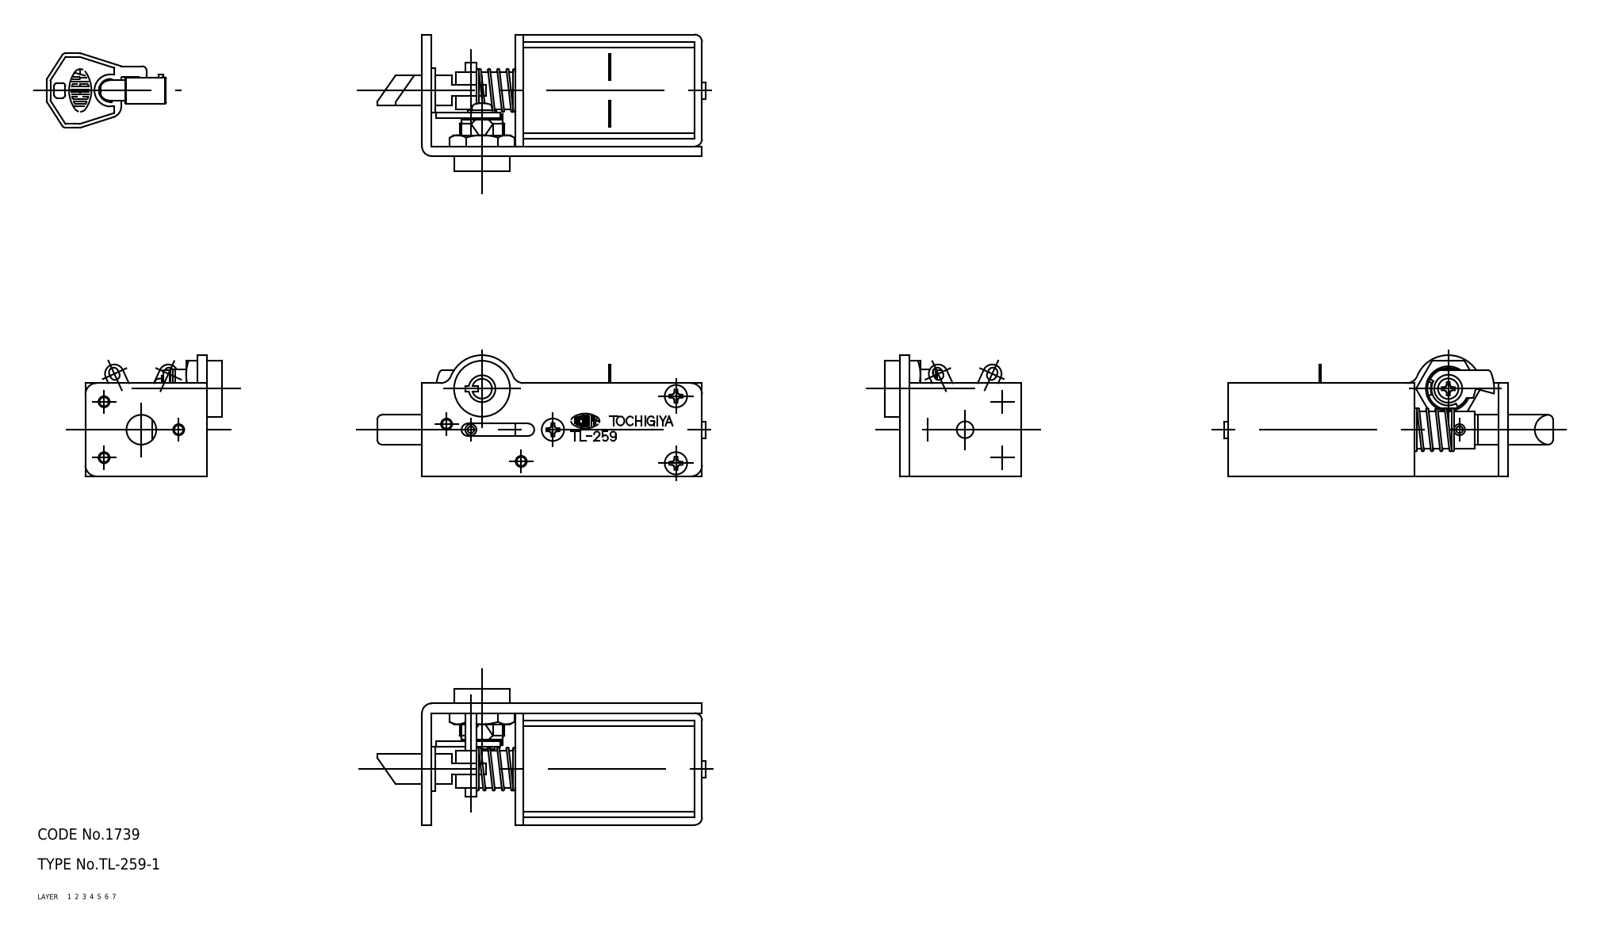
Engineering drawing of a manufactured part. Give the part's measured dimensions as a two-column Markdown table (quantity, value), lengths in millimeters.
| quantity | value |
| --- | --- |
| part name | screw_1; spring; solenoid_2; solenoid_1 (+8 more) |
| STEP written by | CADfix (AUTOMOTIVE_DESIGN) |
| units | millimeters |
| bodies | 15 solids, 394 faces (0 planar, 0 cylindrical, 394 other) |
| overall size | 94.21 × 88 × 32.5 |
| volume | 33 475 mm³ |
| surface area | 23 055 mm² |
